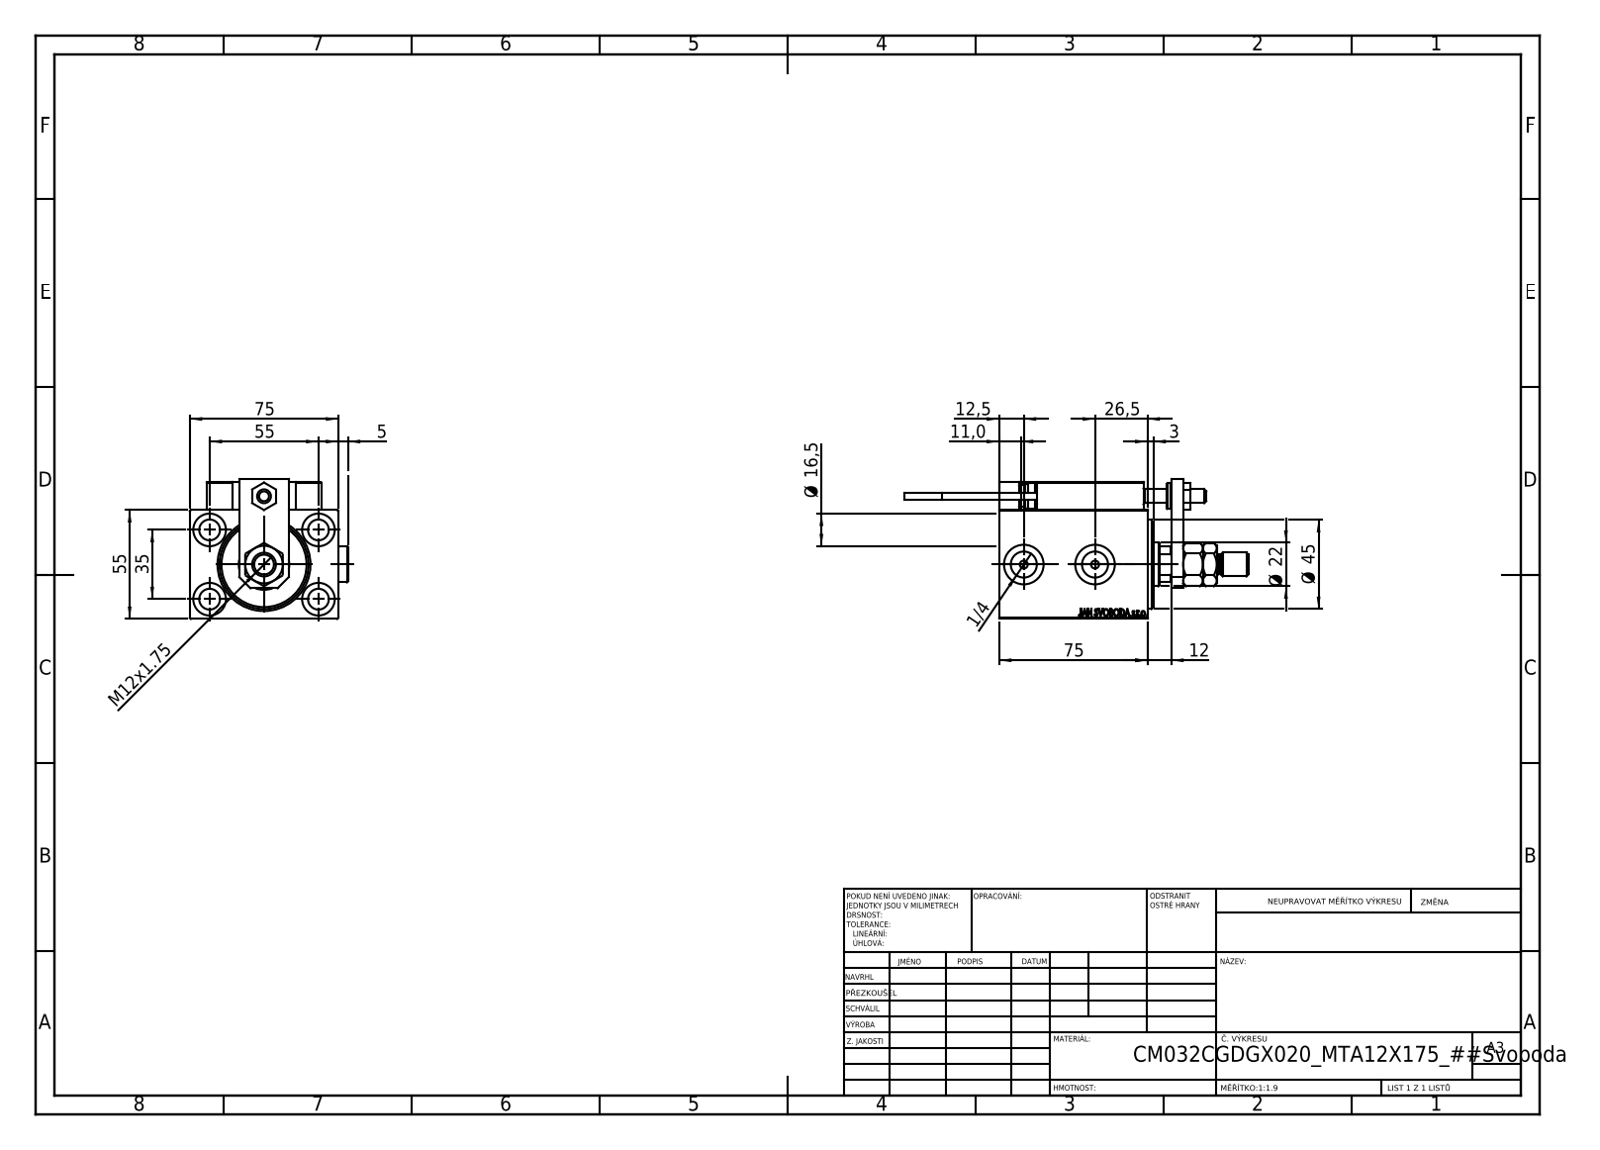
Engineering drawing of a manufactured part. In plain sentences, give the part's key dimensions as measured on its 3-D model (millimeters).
The part is named "Zatka_OIL_PORT; X_Y_MTA; TYC_L79; SWITCH X (+8 more)". Its 3-D file was written by "SolidWorks 2019 (CONFIG_CONTROL_DESIGN)". It is 26 solids with 1385 faces: 609 planar, 208 cylindrical and 568 other. Overall it measures 174 by 79.9 by 70.5 millimeters. Its volume is 318 671 cubic millimeters and its surface area 89 738 square millimeters. Round holes: 6 of diameter 4, 5 of diameter 8, 5 of diameter 10.5, 5 of diameter 16.5, 4 of diameter 3.2, 2 of diameter 5, 2 of diameter 13.16, 2 of diameter 20, 1 of diameter 7, 1 of diameter 22, 1 of diameter 25.5, 1 of diameter 32. Round bosses or shafts: 2 of diameter 18, 2 of diameter 5, 2 of diameter 3.8, 1 of diameter 13, 1 of diameter 12, 1 of diameter 11, 1 of diameter 10. Partial cylindrical surfaces (rounded edges, fillets, slot ends): 30 of radius 0.3, 2 of radius 3, 1 of radius 10.5. The main face-to-face distances are 55, 75, 14, 10, 12, 7, 5, 69, 3, 18. The hole center spacings are 32.6, 11.37, 20, 27.07, 29.59, 29.69, 32.33, 34.83.
